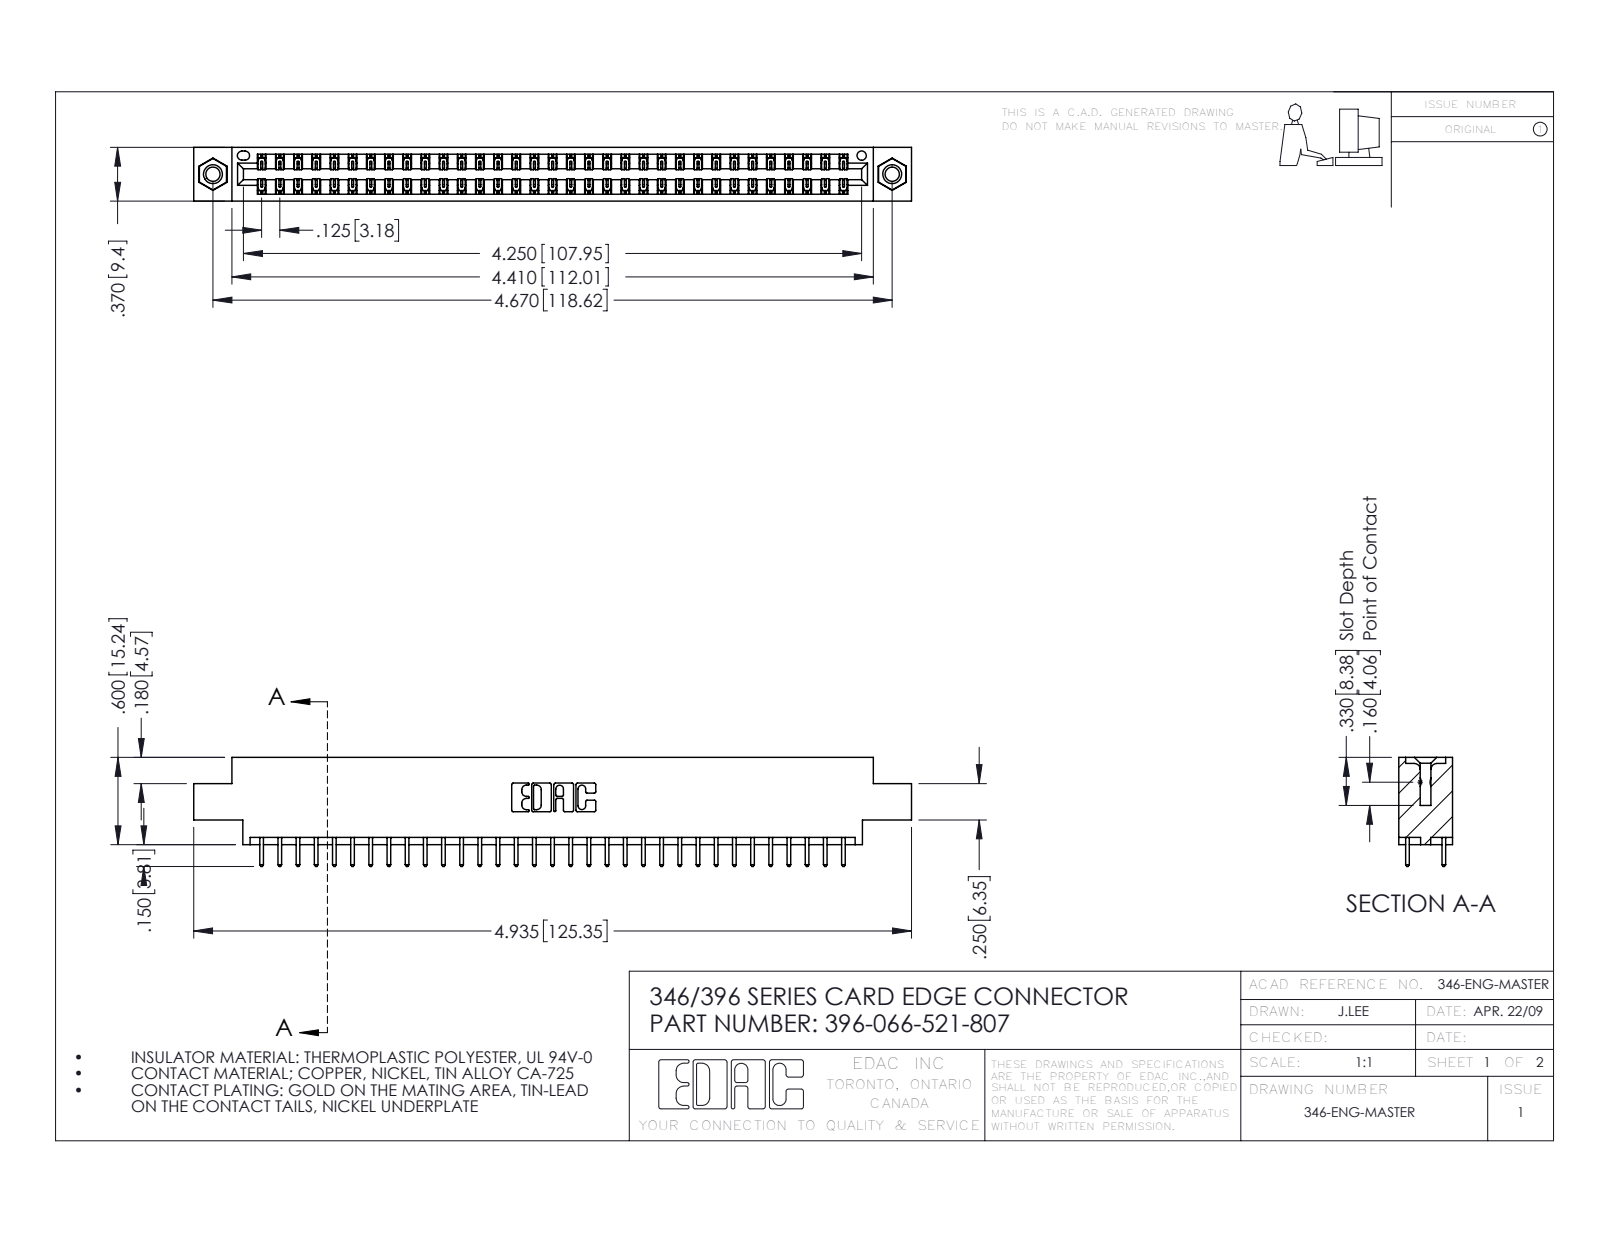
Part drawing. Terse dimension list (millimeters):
name: 346 Part_0.170 Offset - 0.156 Dia-TI; 396-066-521-807; 345-250-001_345-250-005-103; 345-292-001_345-293-121
written by: SolidWorks 2016 (CONFIG_CONTROL_DESIGN)
unit: mm
bodies: 69 solids, 3618 faces (2422 planar, 1180 cylindrical, 16 other)
size: 125.3 × 19.1 × 9.4
volume: 12 000 mm³; area: 16 330 mm²
holes: 2× ⌀2.5, 2× ⌀3.2, 2× ⌀4, 1× ⌀1.6
bosses: 2× ⌀3.9
rounds: 99× R0.2, 66× R0.3, 22× R0.3, 6× R0.2, 6× R0.8, 3× R0.7, 2× R0.4, 2× R0.6
face distances: 1.2, 8.2, 9.4, 6.4, 1.8, 7.6, 0.6, 7, 5.6, 3.8
hole spacings: 6.2, 113.3, 118.6
